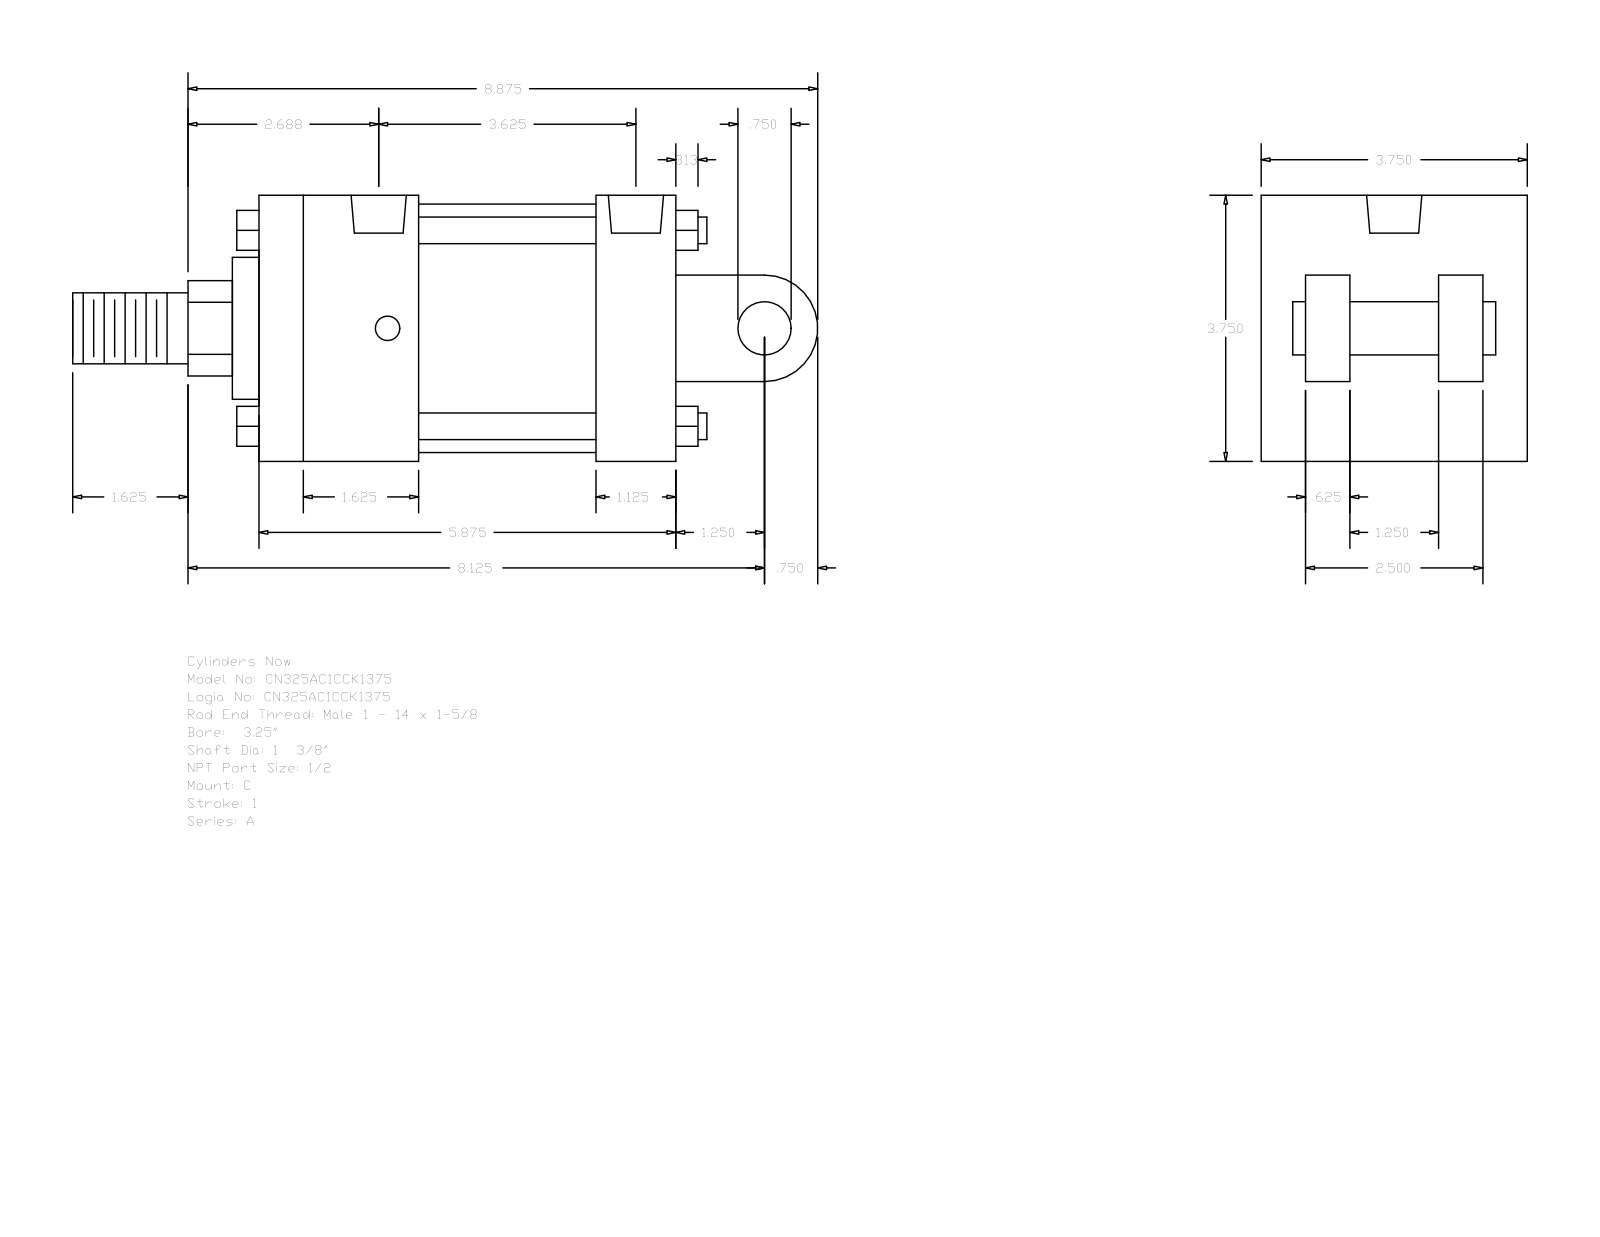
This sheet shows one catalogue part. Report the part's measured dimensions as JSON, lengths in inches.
{"part_name": "A_C__0325_1.375", "step_written_by": "GSSL Pune (CONFIG_CONTROL_DESIGN)", "units": "inches", "bodies": {"solids": 0, "faces": 135, "planar": 102, "cylindrical": 33, "other": 0}, "overall_size": [10.5, 3.75, 3.75], "round_holes": [[0.344, 4], [0.778, 2]], "round_bosses_or_shafts": [[0.375, 4], [3.5, 1], [2, 1], [1.375, 1], [1, 1], [0.75, 1]], "partial_cylinders_radius": [[0.672, 1], [0.75, 1]], "face_to_face_distances": [3.75, 2.5, 5.875, 0.625, 1.125, 2.625, 2.25, 3.125, 1.25, 1.875], "hole_center_spacings": [0.125, 3.375, 3.5, 3.625]}
